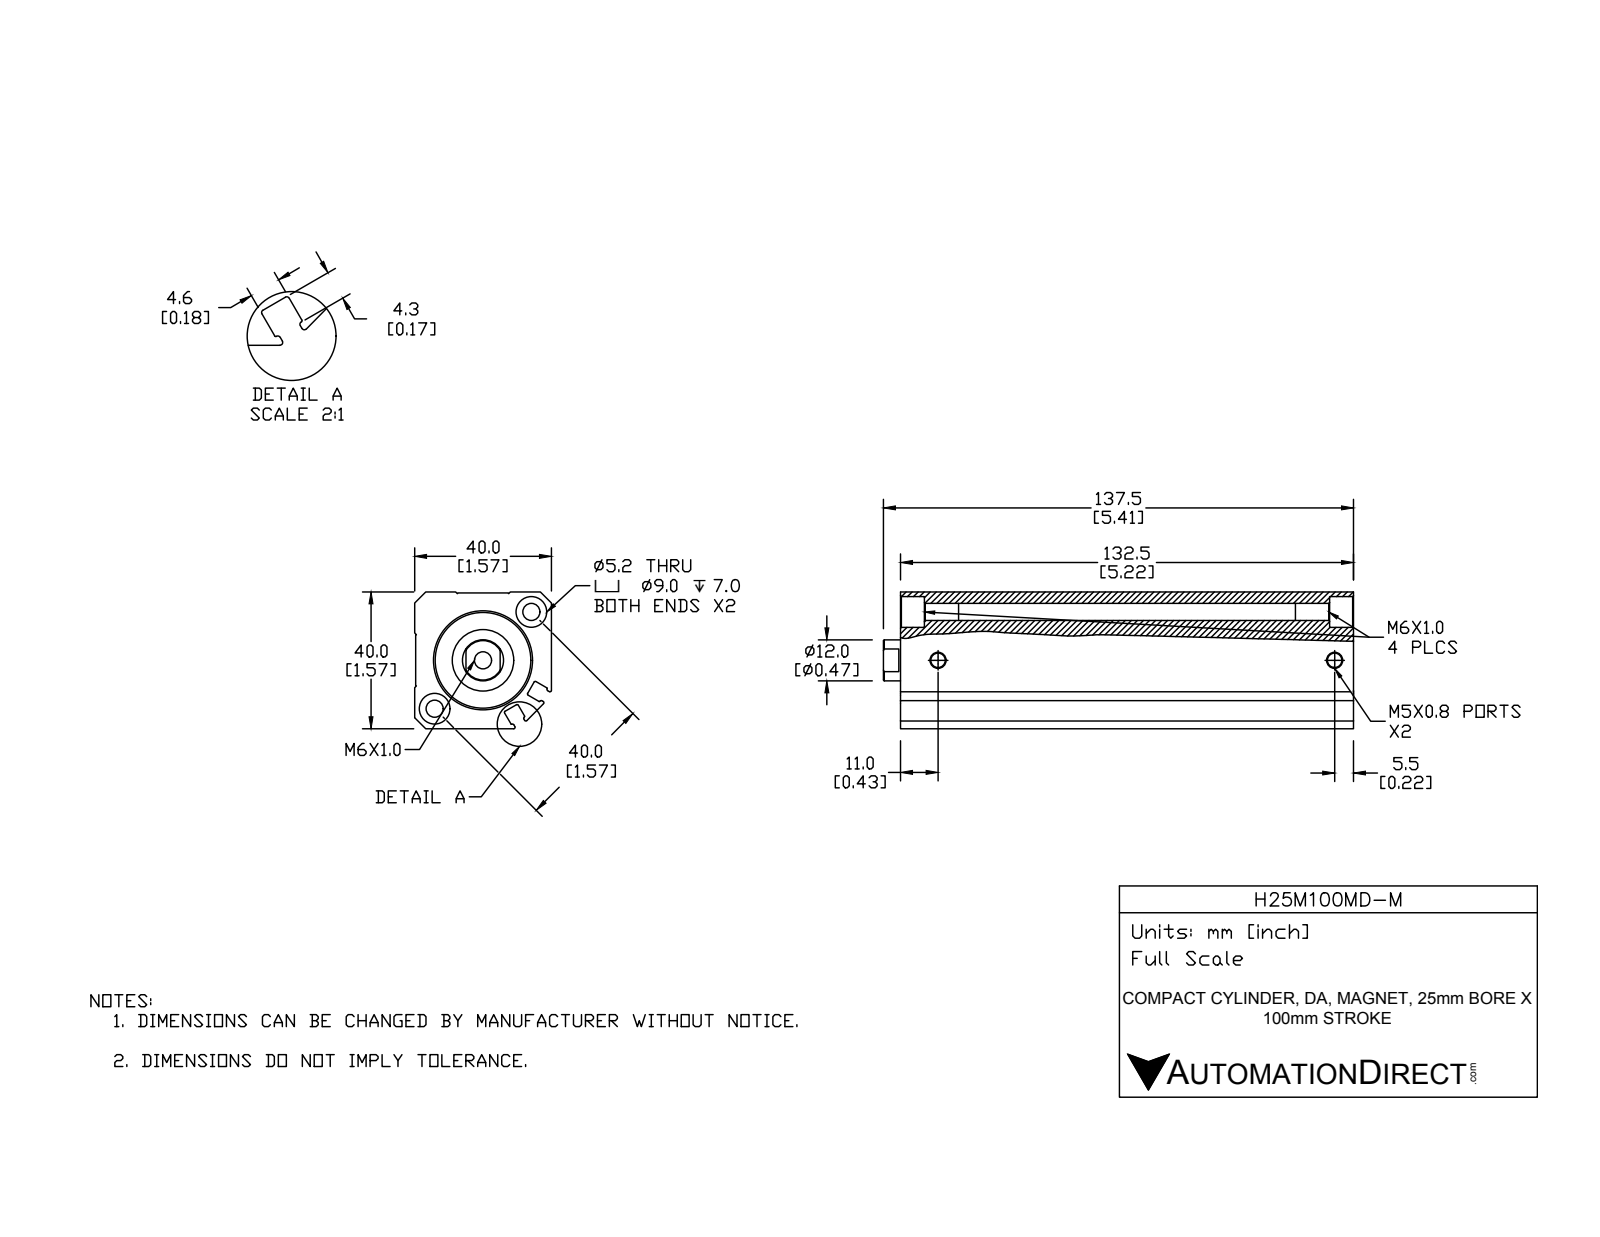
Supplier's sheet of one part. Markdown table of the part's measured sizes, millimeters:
| quantity | value |
| --- | --- |
| part name | H25M100MD-M-PISTON; H25M100MD-M-BODY; H25M100MD-M |
| STEP written by | SolidWorks 2015 (CONFIG_CONTROL_DESIGN) |
| units | millimeters |
| bodies | 2 solids, 141 faces (53 planar, 55 cylindrical, 33 other) |
| overall size | 137.5 × 40 × 40 |
| volume | 149 364 mm³ |
| surface area | 48 380 mm² |
| round holes (diameter × count) | 5 × 3, 4.2 × 2, 9 × 2, 12 × 1, 16 × 1, 25 × 1, 28 × 1 |
| round bosses / shafts (diameter × count) | 18 × 1, 14 × 1 |
| partial cylindrical surfaces (radius × count) | 0.4 × 12, 0.2 × 4 |
| main face-to-face distances | 40, 39.7, 4, 4.6, 132.5, 128.5, 52, 1.4, 2.6, 131.1 |
| hole center spacings | 20, 39.99, 116 |
